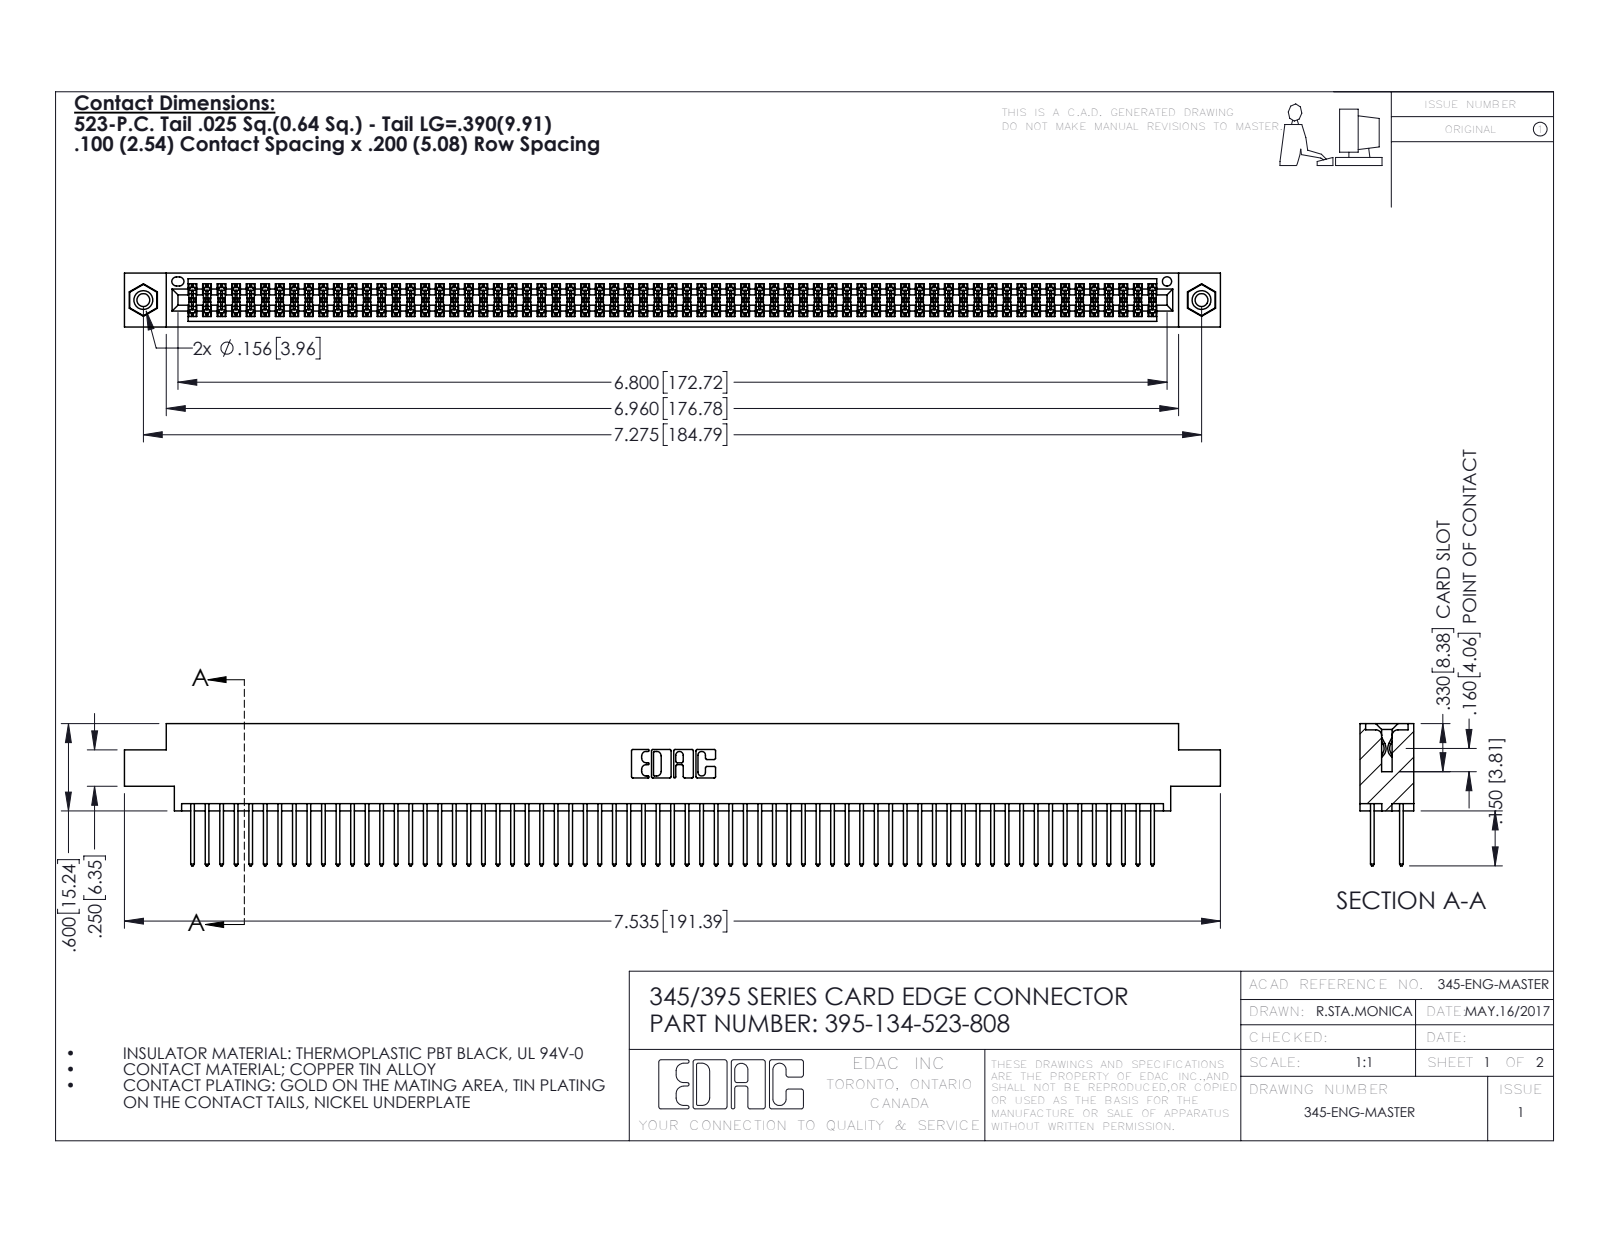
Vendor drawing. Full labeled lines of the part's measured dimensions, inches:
Part name (STEP PRODUCT): 345-250-001_345-250-003-102; 395-134-523-808; 345 Part_0.170 Offset - 0.156 Dia-TI; 345-292-001_345-293-123
STEP written by: SolidWorks 2016 (CONFIG_CONTROL_DESIGN)
Units: inches
Bodies: 137 solids, 6890 faces (4538 planar, 2336 cylindrical, 16 other)
Overall size (bounding box): 7.535 × 0.977 × 0.37
Volume: 1.158 in³ · Surface area: 46.39 in²
Round holes (diameter × count): ⌀0.089 ×2, ⌀0.125 ×2, ⌀0.156 ×2, ⌀0.064 ×1
Round bosses / shafts (diameter × count): ⌀0.155 ×2
Partial cylindrical surfaces — rounded edges, fillets, slot ends (radius × count): R0.006 ×201, R0.01 ×134, R0.01 ×22, R0.007 ×6, R0.031 ×6, R0.026 ×3, R0.014 ×2, R0.019 ×2
Main face-to-face distances: 0.072, 0.298, 0.2, 0.098, 0.272, 0.025, 0.37, 0.225, 0.175, 0.149
Hole centre spacings: 0.27, 7.039, 7.275
